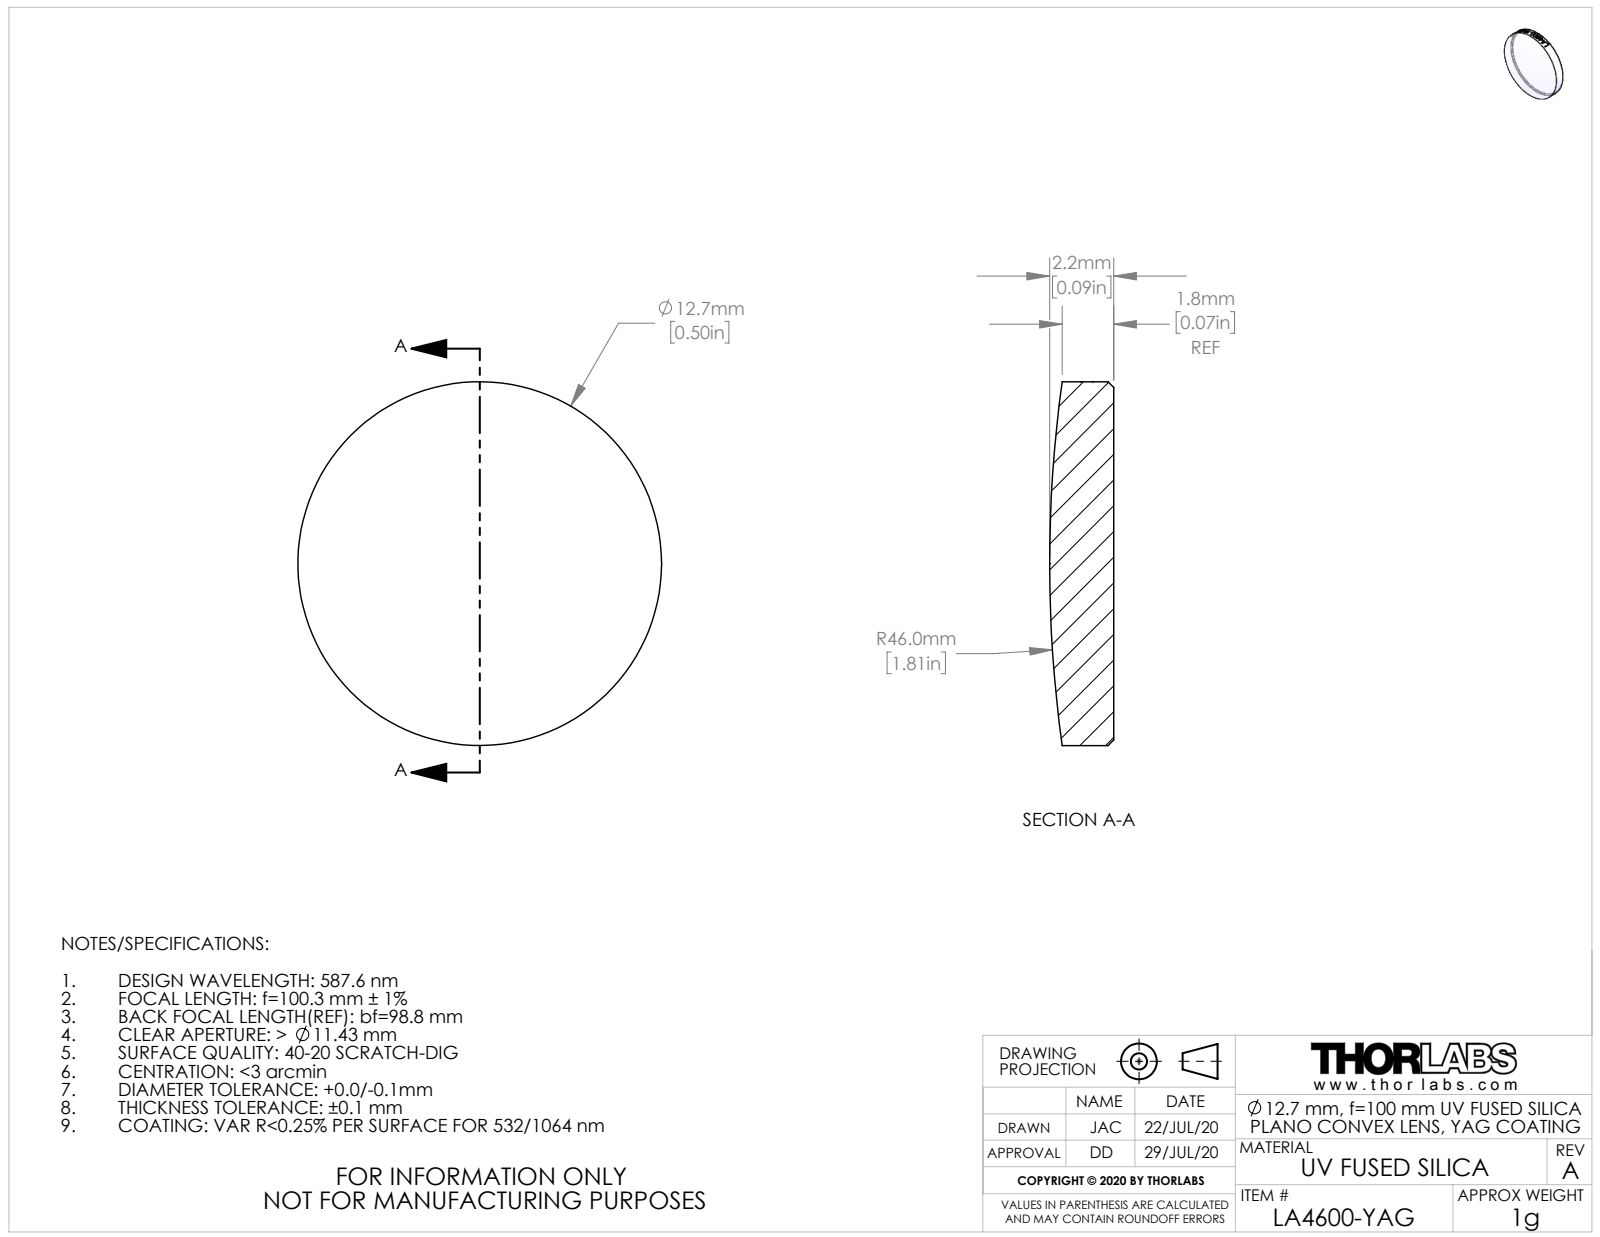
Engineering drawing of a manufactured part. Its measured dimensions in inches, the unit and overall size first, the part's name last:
Units: inches
Overall size (bounding box): 0.5 × 0.5 × 0.088
Round bosses / shafts (diameter × count): ⌀0.5 ×1
Volume: 0.016 in³ · Surface area: 0.498 in²
Bodies: 1 solid, 27 faces (1 planar, 22 cylindrical, 4 other)
Part name (STEP PRODUCT): TTN217851-E0W
STEP written by: SolidWorks 2018 (CONFIG_CONTROL_DESIGN)
